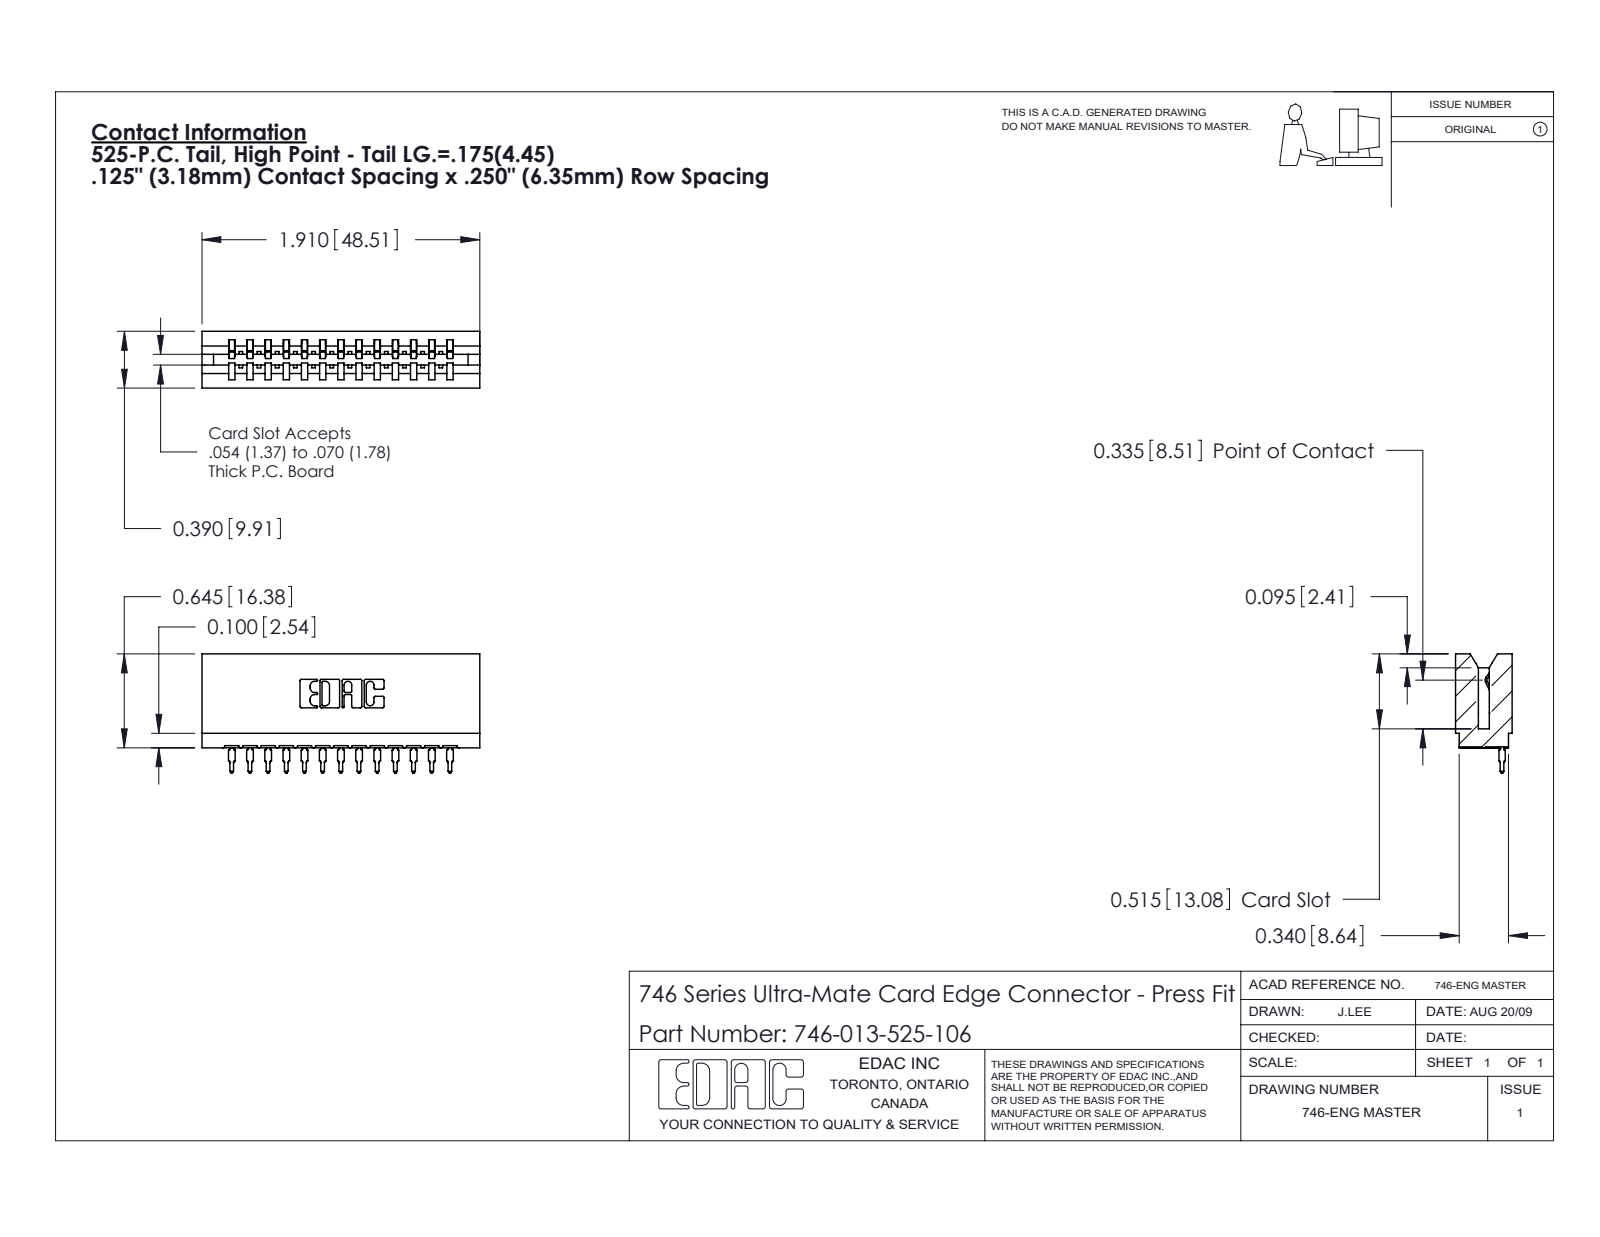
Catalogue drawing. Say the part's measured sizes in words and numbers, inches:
The part is named "746-013-525-106; 746-292-001_525; 746 Part_.515 Slot Depth - 06". Its 3-D file was written by "SolidWorks 2020 (CONFIG_CONTROL_DESIGN)". It is 14 solids with 1502 faces: 875 planar, 289 cylindrical and 338 other. Overall it measures 1.91 by 0.819 by 0.39 inches. Its volume is 0.319 cubic inches and its surface area 11.18 square inches. Partial cylindrical surfaces (rounded edges, fillets, slot ends): 26 of radius 0.021, 22 of radius 0.01, 14 of radius 0.015, 6 of radius 0.007, 6 of radius 0.031, 4 of radius 0.005, 4 of radius 0.011, 3 of radius 0.026. The main face-to-face distances are 0.25, 0.333, 0.057, 0.5, 0.39, 0.125, 0.125, 0.292, 0.75, 0.042.
